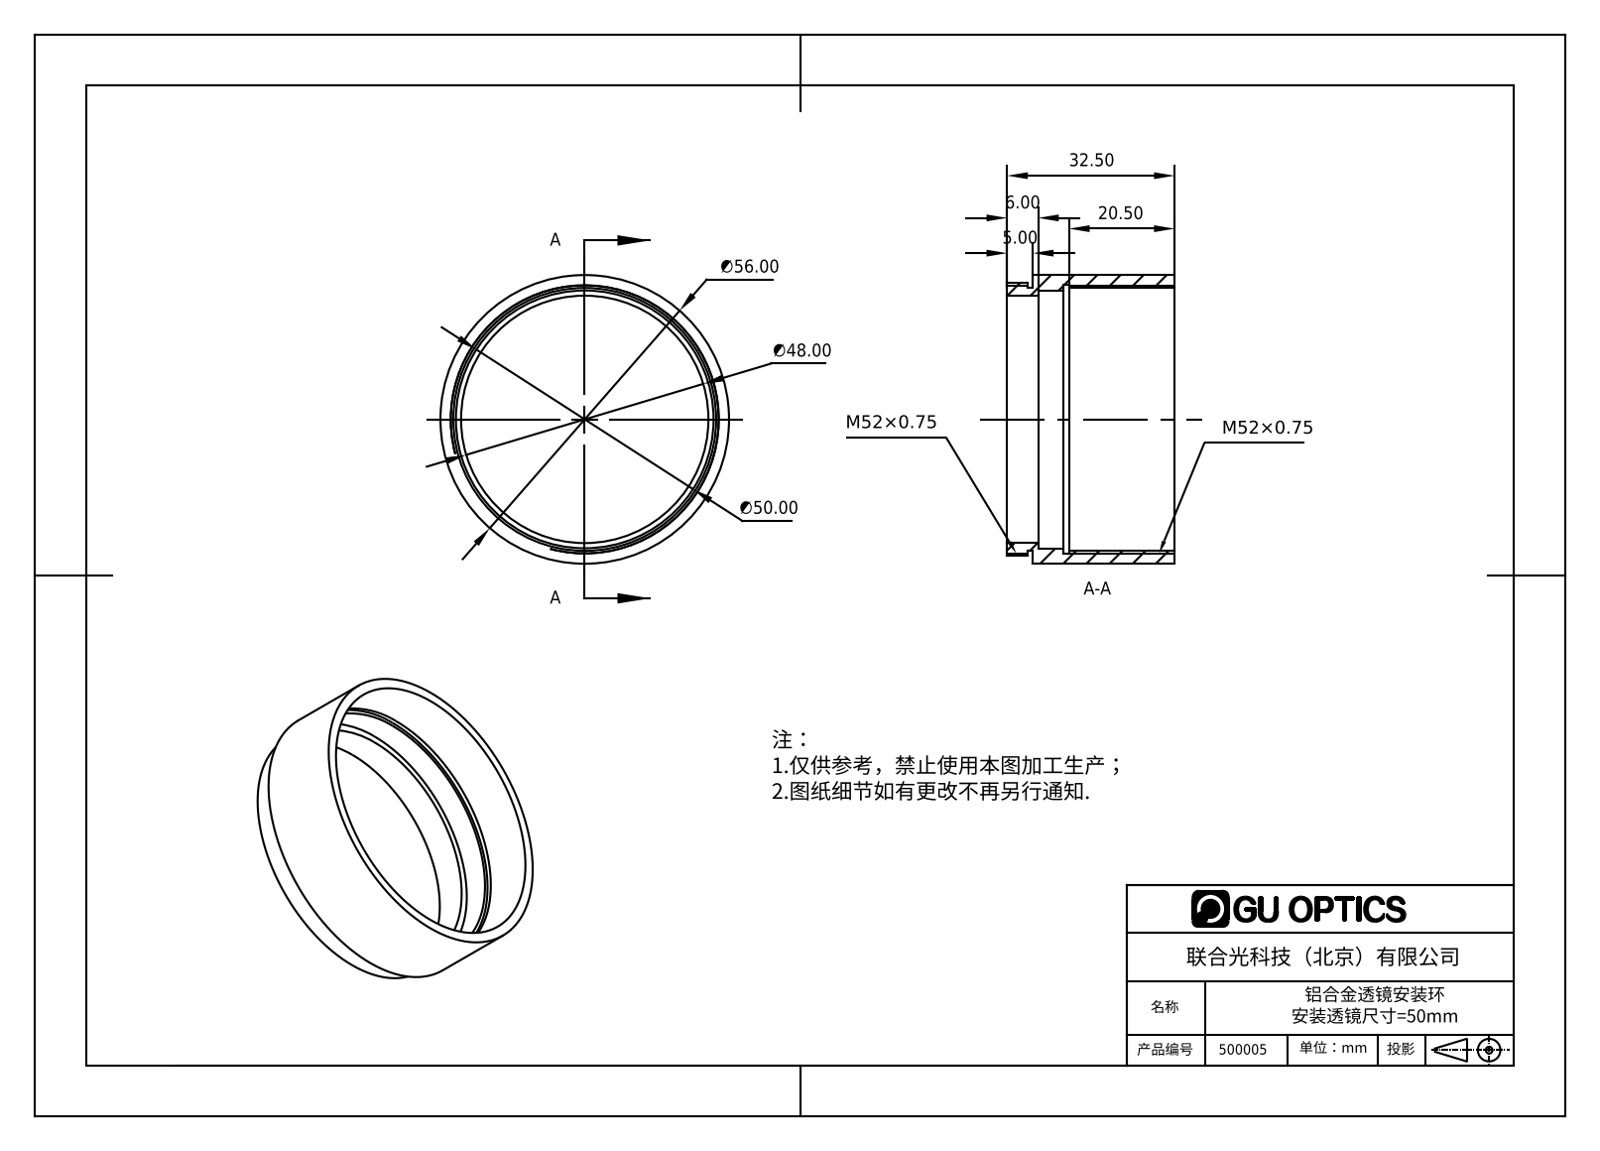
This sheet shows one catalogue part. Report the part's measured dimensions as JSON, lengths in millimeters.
{"part_name": "500005", "step_written_by": "SolidWorks 2016 (CONFIG_CONTROL_DESIGN)", "units": "millimeters", "bodies": {"solids": 1, "faces": 21, "planar": 7, "cylindrical": 14, "other": 0}, "overall_size": [56, 56, 32.5], "volume_mm3": 13908, "surface_area_mm2": 12631, "round_holes": [[48, 1], [50, 1], [51, 1], [52.2, 1]], "round_bosses_or_shafts": [[56, 1], [53, 1]], "face_to_face_distances": [5, 6, 27.5, 1, 32.5, 7, 11, 21.5, 4, 28.5]}
